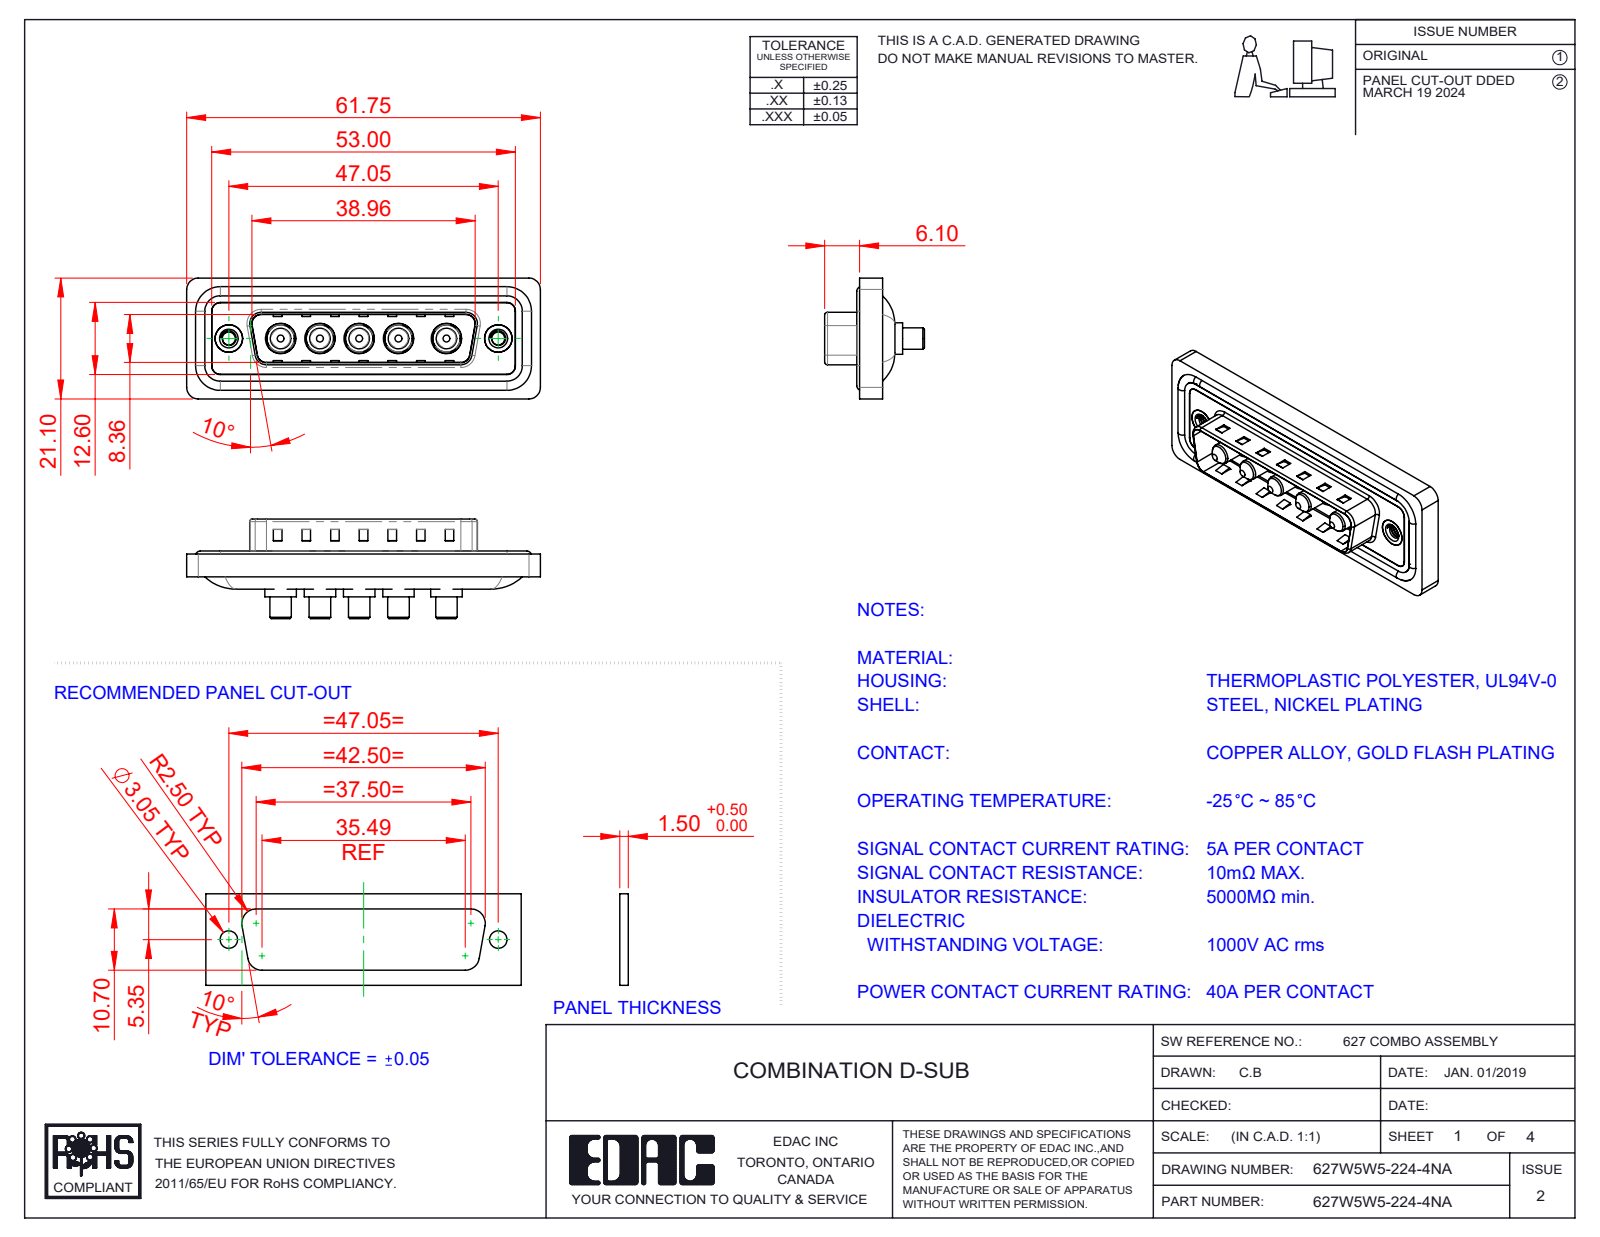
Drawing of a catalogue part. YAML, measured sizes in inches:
part_name: "627Combo Shell Rear_25 Contacts; 627W5W5-224-4NA; 627Combo Housing_5W5; 627Combo Shell Front_25 Contacts (+3 more)"
step_written_by: "SolidWorks 2023 (CONFIG_CONTROL_DESIGN)"
units: inches
bodies: {solids: 17, faces: 676, planar: 259, cylindrical: 285, other: 132}
overall_size: [2.431, 0.831, 0.685]
volume: 0.462
surface_area: 18.36
round_holes:
  - {diameter: 0.191, count: 5}
  - {diameter: 0.209, count: 5}
  - {diameter: 0.089, count: 2}
  - {diameter: 0.157, count: 2}
  - {diameter: 0.189, count: 2}
  - {diameter: 0.197, count: 2}
round_bosses_or_shafts:
  - {diameter: 0.217, count: 5}
  - {diameter: 0.205, count: 5}
  - {diameter: 0.187, count: 5}
  - {diameter: 0.148, count: 5}
  - {diameter: 0.142, count: 5}
  - {diameter: 0.063, count: 4}
  - {diameter: 0.193, count: 2}
partial_cylinders:
  - {radius: 0.059, count: 22}
  - {radius: 0.079, count: 18}
  - {radius: 0.02, count: 8}
  - {radius: 0.063, count: 8}
  - {radius: 0.083, count: 5}
  - {radius: 0.01, count: 4}
  - {radius: 0.024, count: 4}
  - {radius: 0.026, count: 4}
face_to_face_distances: [0.016, 0.059, 0.02, 0.043, 0.122, 0.063, 0.114, 0.032, 0.377, 0.222]
hole_center_spacings: [0.27, 0.356, 0.541, 1.496, 0.27, 0.33, 0.33, 0.356]
